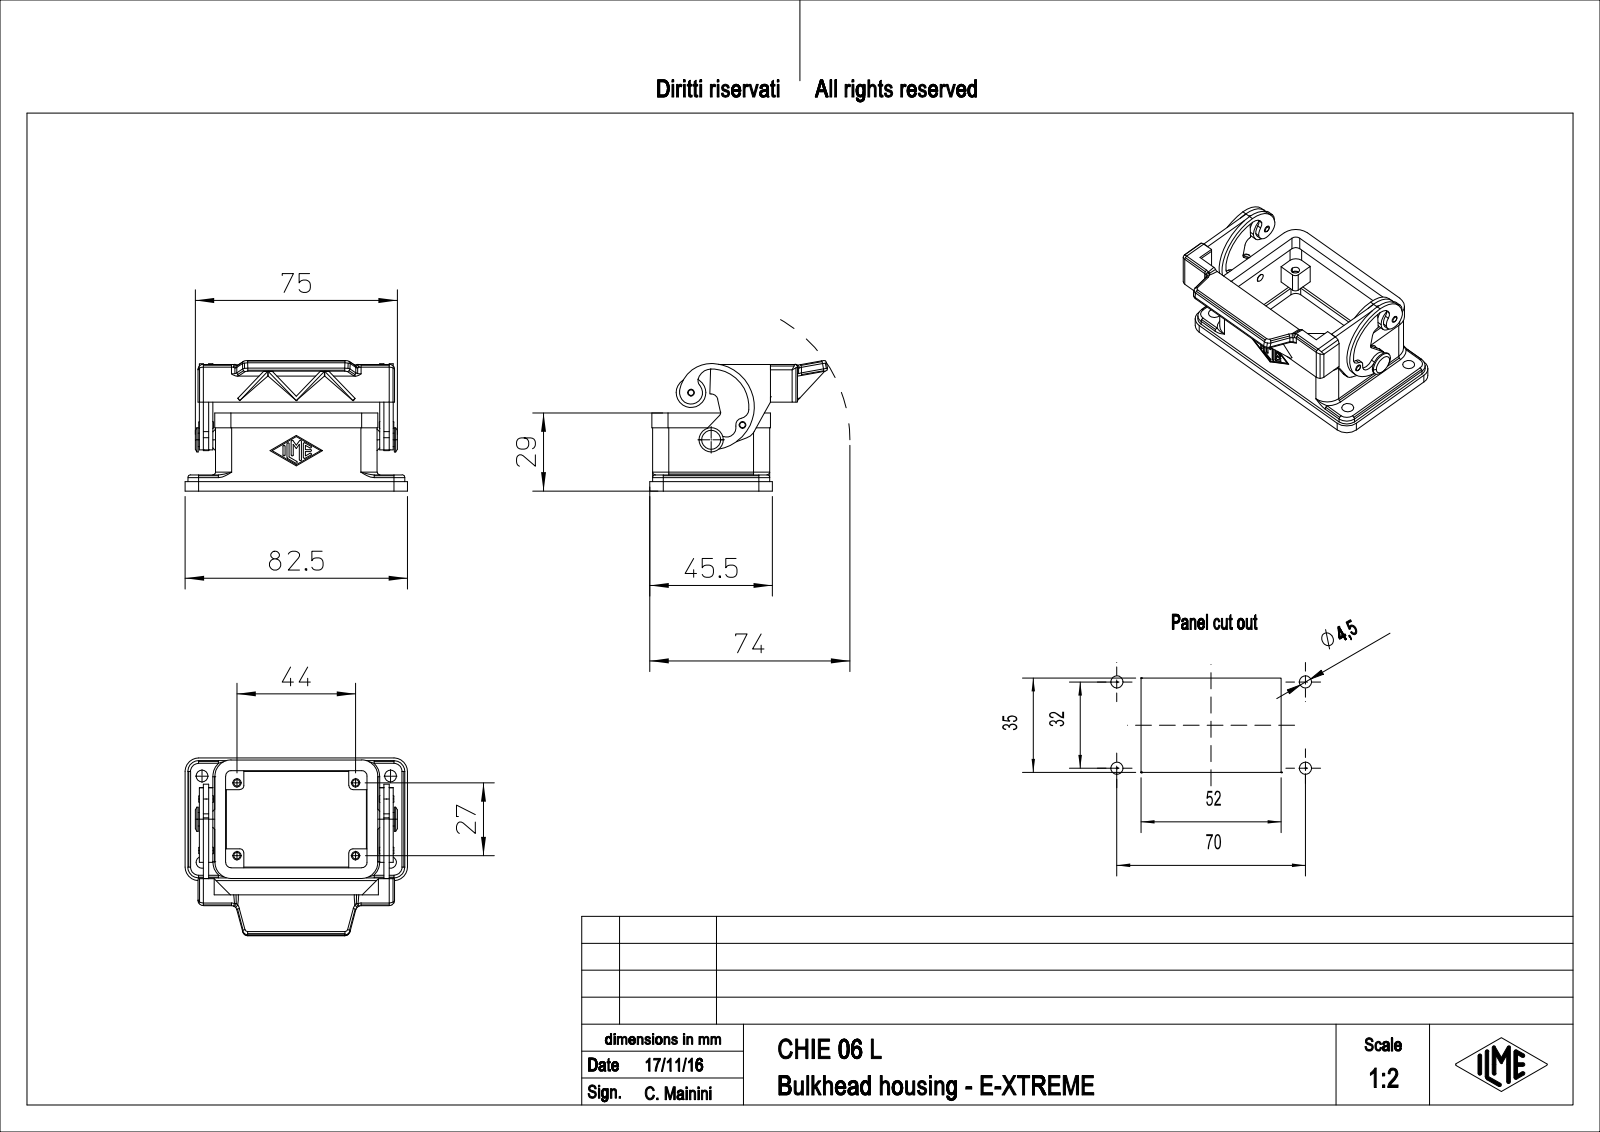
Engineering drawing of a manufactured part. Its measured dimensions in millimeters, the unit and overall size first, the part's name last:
Units: millimetres
Overall size (bounding box): 82.5 × 65.95 × 48.42
Round holes (diameter × count): ⌀2.46 ×4, ⌀3.1 ×4, ⌀4.4 ×4, ⌀2.5 ×1
Round bosses / shafts (diameter × count): ⌀11 ×1, ⌀9 ×1, ⌀5 ×1, ⌀3 ×1, ⌀2 ×1
Partial cylindrical surfaces — rounded edges, fillets, slot ends (radius × count): R0.38 ×14, R1 ×13, R2 ×12, R6 ×8, R2.5 ×7, R5 ×6, R1.5 ×5, R4 ×5
Main face-to-face distances: 4, 3, 40.5, 1, 0.75, 67, 5.5, 2.5, 3.5, 6
Hole centre spacings: 13.24, 32.24, 57.05, 64.18, 27, 32, 44, 51.62
Volume: 37 031 mm³ · Surface area: 25 357 mm²
Bodies: 1 solid, 472 faces (212 planar, 200 cylindrical, 60 other)
Part name (STEP PRODUCT): CHIE_06_L
STEP written by: PTC Creo Elements/Direct Modeling 19.0E 27-Jun-2016 (C) Parametric Technology GmbH (AUTOMOTIVE_DESIGN)
